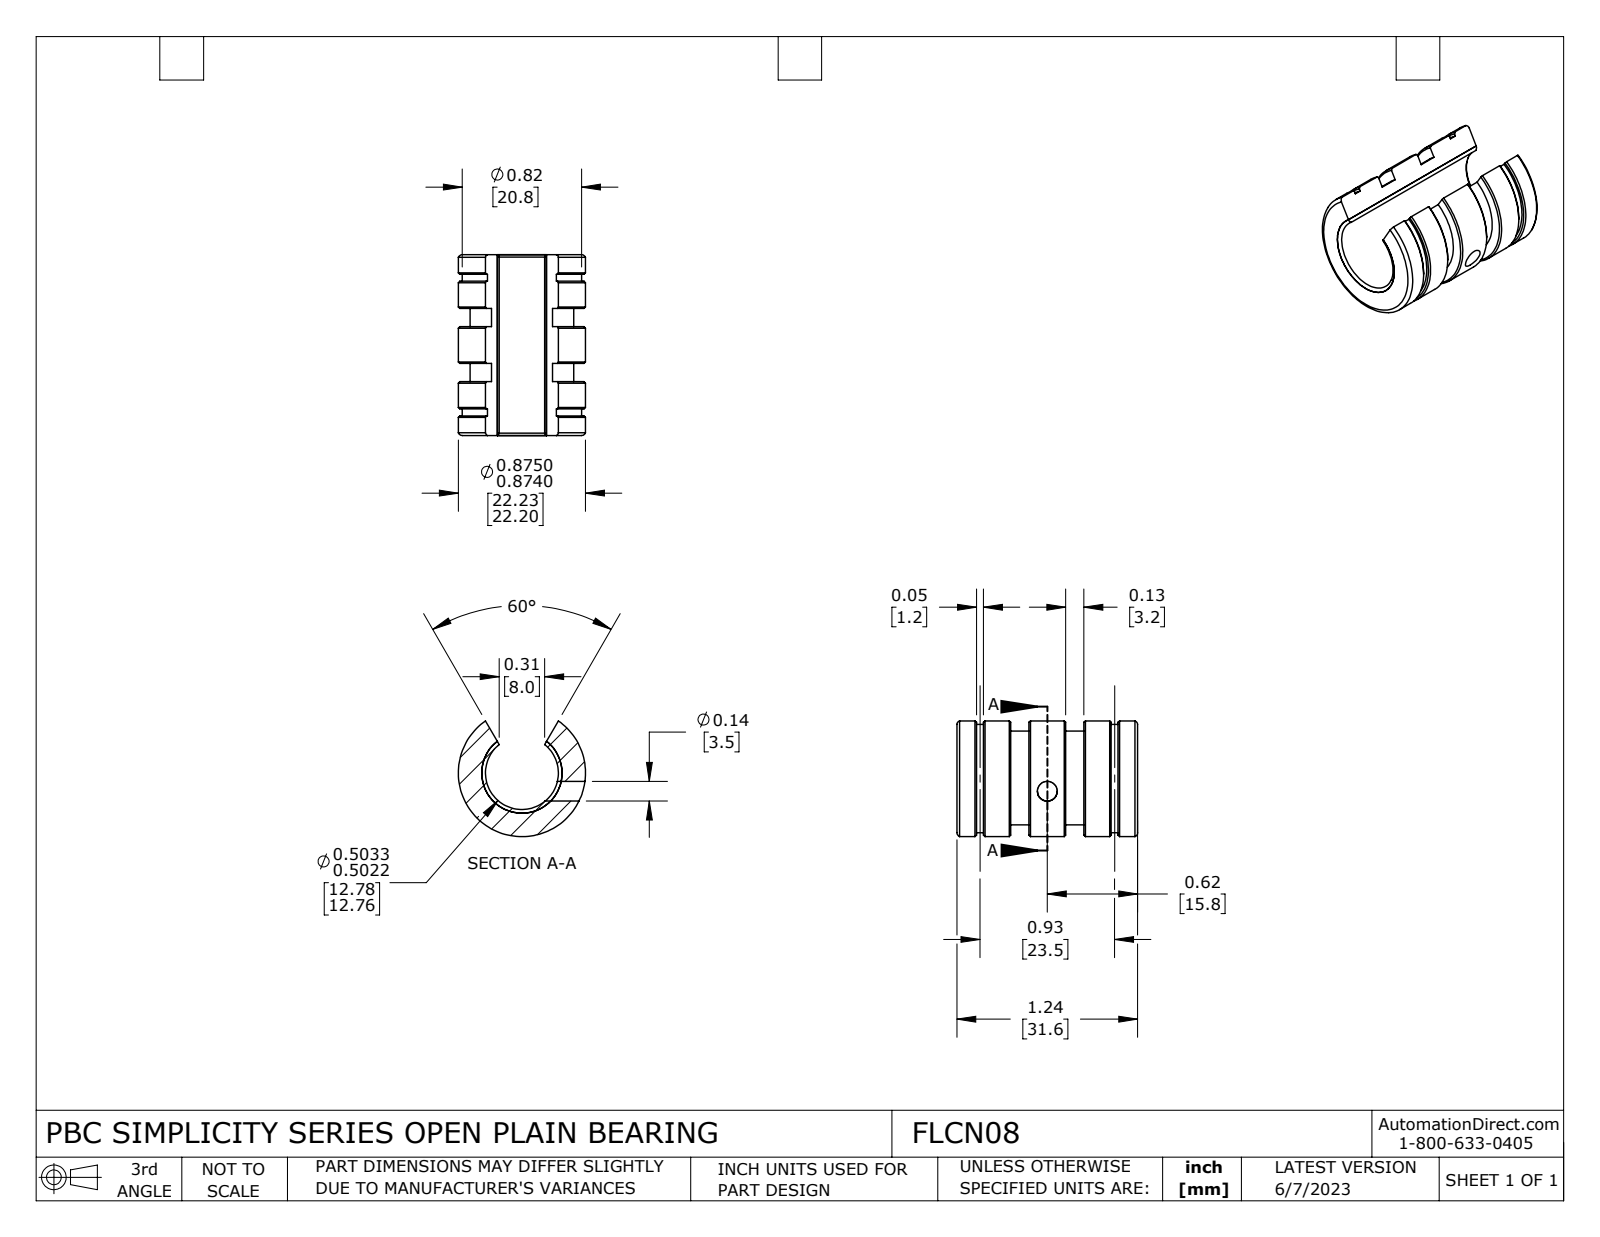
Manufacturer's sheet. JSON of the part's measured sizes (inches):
{"part_name": "FLCN08", "step_written_by": "SolidWorks 2021 (CONFIG_CONTROL_DESIGN)", "units": "inches", "bodies": {"solids": 2, "faces": 82, "planar": 14, "cylindrical": 40, "other": 28}, "overall_size": [1.243, 0.874, 0.795], "volume_in3": 0.349, "surface_area_in2": 9.352, "round_holes": [[0.136, 1]], "round_bosses_or_shafts": [[0.874, 1], [0.82, 1], [0.712, 1]], "partial_cylinders_radius": [[0.25, 1], [0.276, 1]], "face_to_face_distances": [0.495, 0.748, 0.37, 0.873, 0.125, 0.378, 1.243, 0.253, 0.503, 0.135]}
